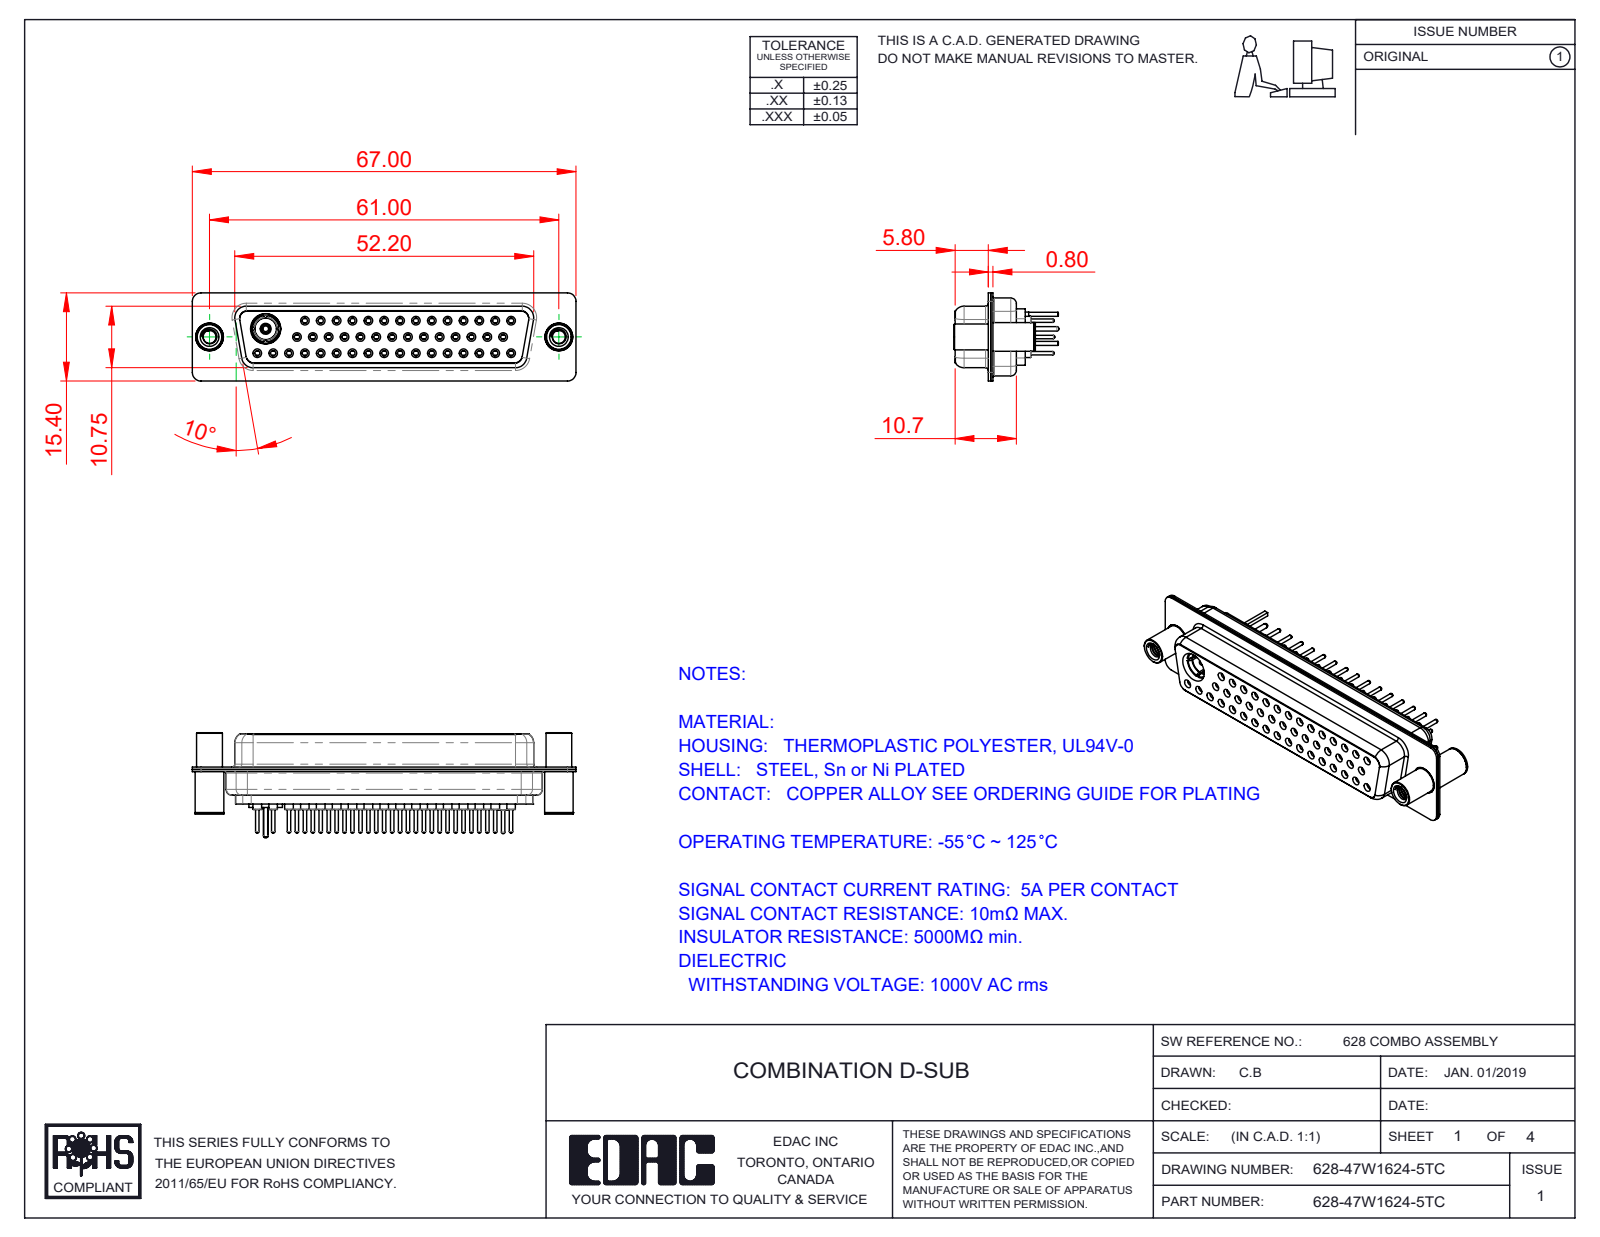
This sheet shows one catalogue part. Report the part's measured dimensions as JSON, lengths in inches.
{"part_name": "Co-Ax Plug Assy_St; Locking Collar; 628-47W1624-5TC; Co-Ax Plug_Straight PC Tail (+8 more)", "step_written_by": "SolidWorks 2016 (CONFIG_CONTROL_DESIGN)", "units": "inches", "bodies": {"solids": 55, "faces": 3027, "planar": 817, "cylindrical": 1120, "other": 1090}, "overall_size": [2.638, 0.722, 0.606], "volume_in3": 0.448, "surface_area_in2": 23.88, "round_holes": [[0.043, 47], [0.059, 46], [0.035, 45], [0.079, 45], [0.063, 31], [0.067, 14], [0.191, 3], [0.089, 2], [0.128, 2], [0.157, 2], [0.159, 2], [0.111, 1]], "round_bosses_or_shafts": [[0.087, 46], [0.024, 46], [0.063, 15], [0.197, 3], [0.195, 2], [0.189, 2], [0.177, 2], [0.23, 1]], "partial_cylinders_radius": [[0.059, 16], [0.053, 12], [0.079, 12], [0.063, 8], [0.01, 4], [0.02, 4], [0.024, 4], [0.026, 4]], "face_to_face_distances": [0.016, 0.238, 0.446, 0.254, 0.074, 0.482, 0.244, 0.228, 0.407, 0.43], "hole_center_spacings": [0.124, 0.109, 0.218, 0.327, 0.436, 0.545, 0.654, 0.763]}
